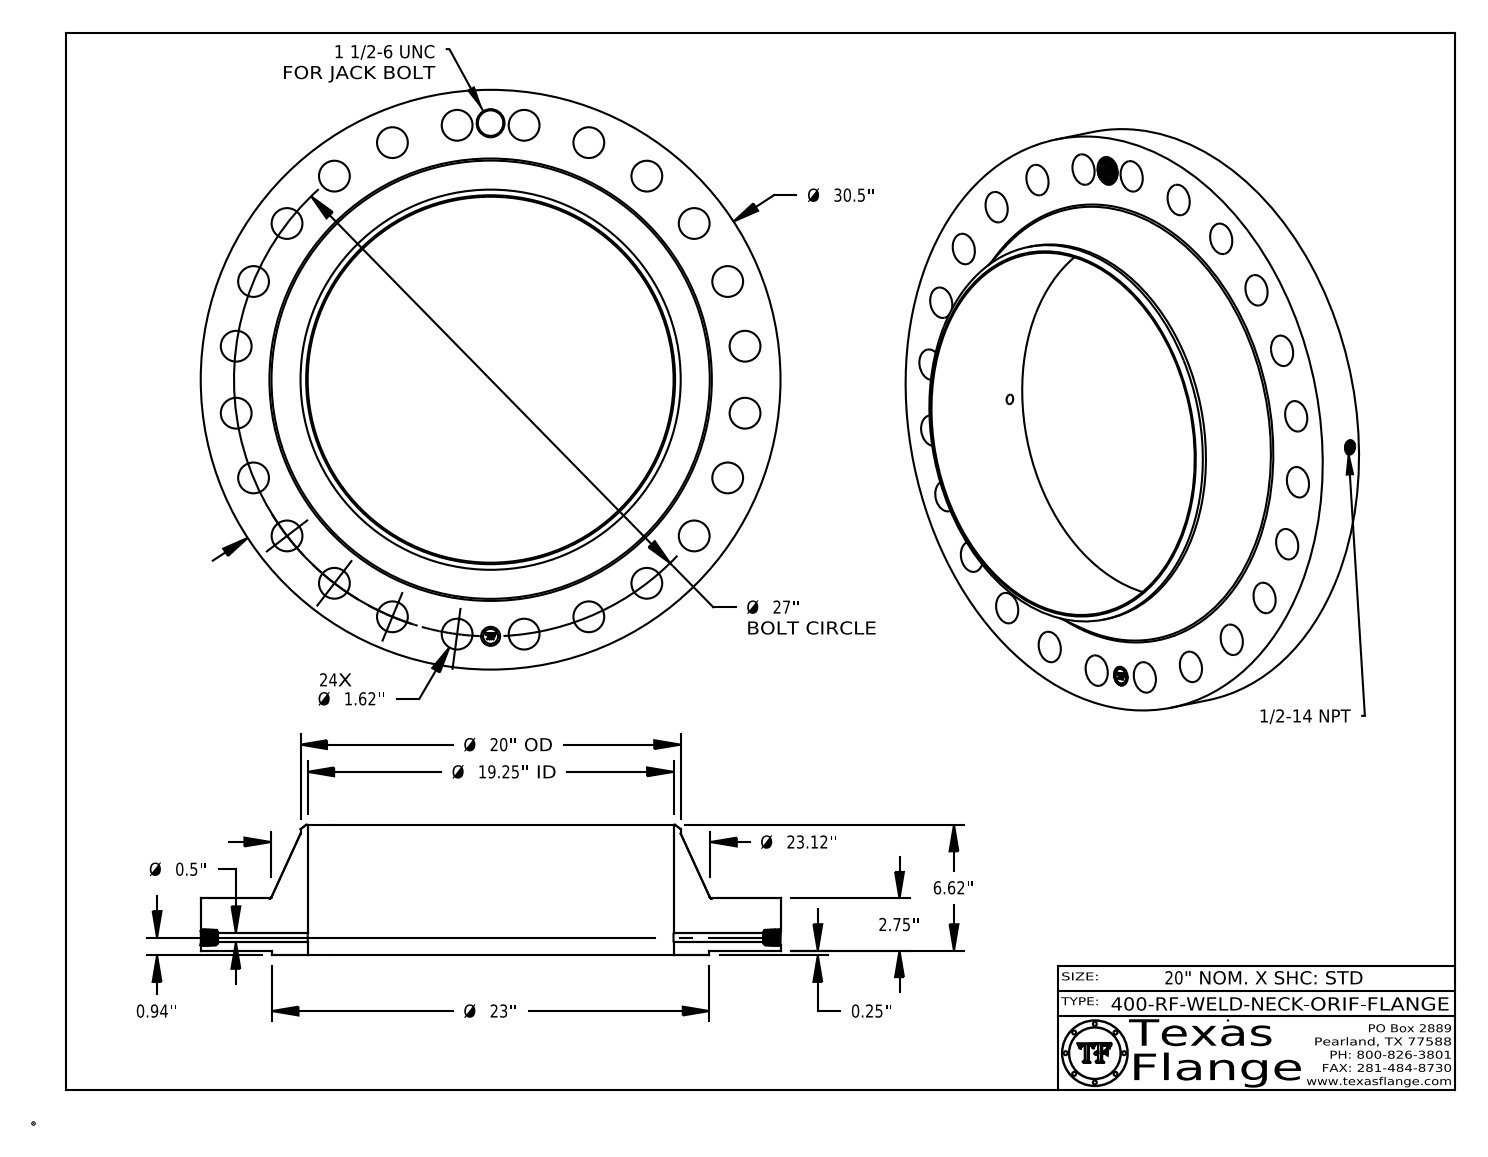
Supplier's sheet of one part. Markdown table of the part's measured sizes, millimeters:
| quantity | value |
| --- | --- |
| part name | 400-RF-WELD-NECK |
| STEP written by | CATIA V5 STEP AP214 (AUTOMOTIVE_DESIGN) |
| units | millimeters |
| bodies | 1 solid, 810 faces (369 planar, 129 cylindrical, 312 other) |
| overall size | 774.7 × 774.7 × 174.5 |
| volume | 22 290 000 mm³ |
| surface area | 1 299 000 mm² |
| round holes (diameter × count) | 41.1 × 24, 12.7 × 1, 17.1 × 1, 25.4 × 1, 34.1 × 1, 489 × 1 |
| round bosses / shafts (diameter × count) | 1.5 × 8, 774.7 × 1, 584.2 × 1, 508 × 1, 20 × 1 |
| main face-to-face distances | 69.9, 6.4, 76.2, 174.5, 168.1, 98.3, 75.8, 69.5, 0.4, 98.7 |
| hole center spacings | 342.9, 593.9, 633.6, 544.1, 89.5, 177.5, 484.9, 662.4 |
